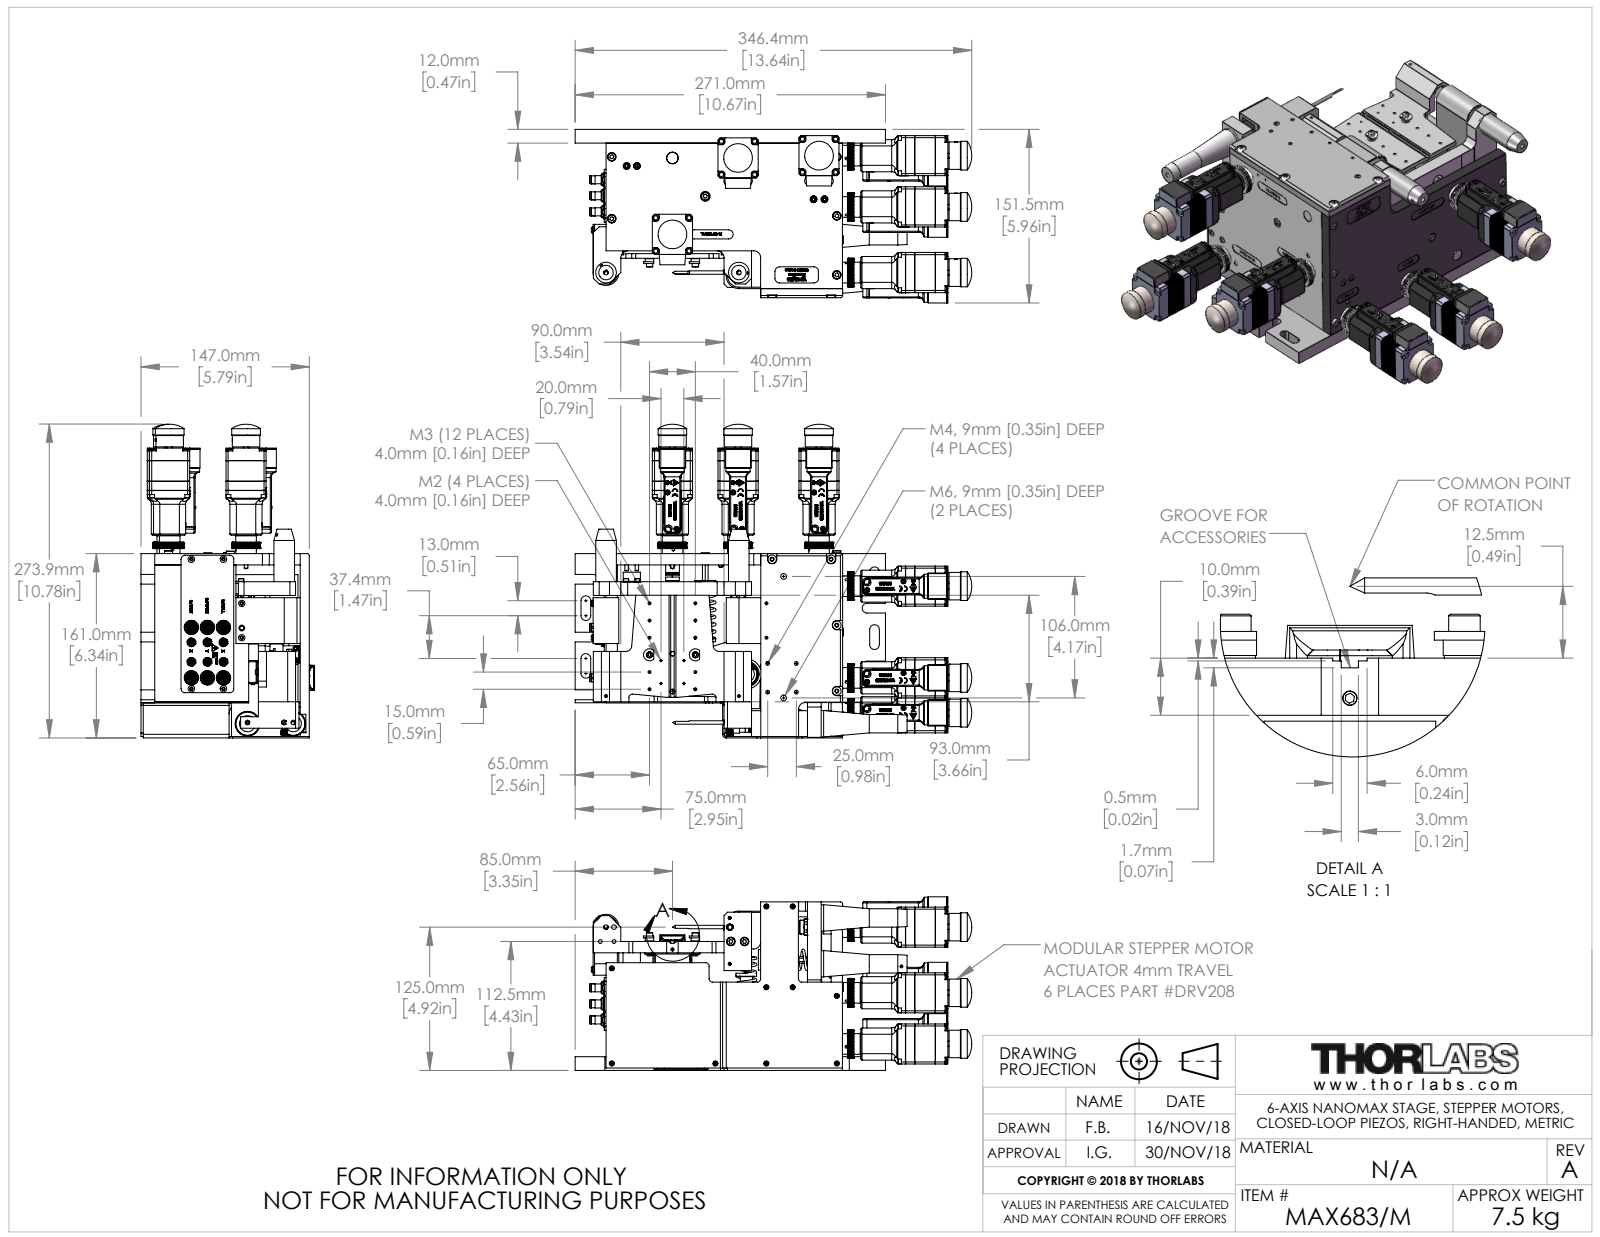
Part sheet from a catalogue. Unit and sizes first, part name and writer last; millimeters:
Units: millimetres
Overall size (bounding box): 346.4 × 273.9 × 151.5
Round holes (diameter × count): ⌀2.5 ×115, ⌀1.6 ×50, ⌀3.2 ×48, ⌀0.6 ×42, ⌀3.3 ×42, ⌀2.05 ×28, ⌀4.5 ×26, ⌀3.4 ×24, ⌀2.2 ×18, ⌀3.5 ×18, ⌀7.5 ×15, ⌀2.8 ×14
Round bosses / shafts (diameter × count): ⌀3 ×87, ⌀5.5 ×74, ⌀0.8 ×42, ⌀0.47 ×42, ⌀4 ×39, ⌀0.94 ×36, ⌀2 ×34, ⌀7 ×32
Partial cylindrical surfaces — rounded edges, fillets, slot ends (radius × count): R0.1 ×122, R2 ×98, R5 ×70, R2.6 ×66, R3.26 ×66, R0.45 ×60, R3 ×50, R0.2 ×48
Main face-to-face distances: 12, 10, 30.5, 1.2, 196.5, 8, 53.5, 127, 18, 91
Hole centre spacings: 50, 15, 42.72, 30, 40, 9.5, 45, 60.21
Volume: 2 094 000 mm³ · Surface area: 863 161 mm²
Bodies: 596 solids, 25034 faces (12502 planar, 7387 cylindrical, 5145 other)
Part name (STEP PRODUCT): MAX683_M
STEP written by: SolidWorks 2018 (CONFIG_CONTROL_DESIGN)
